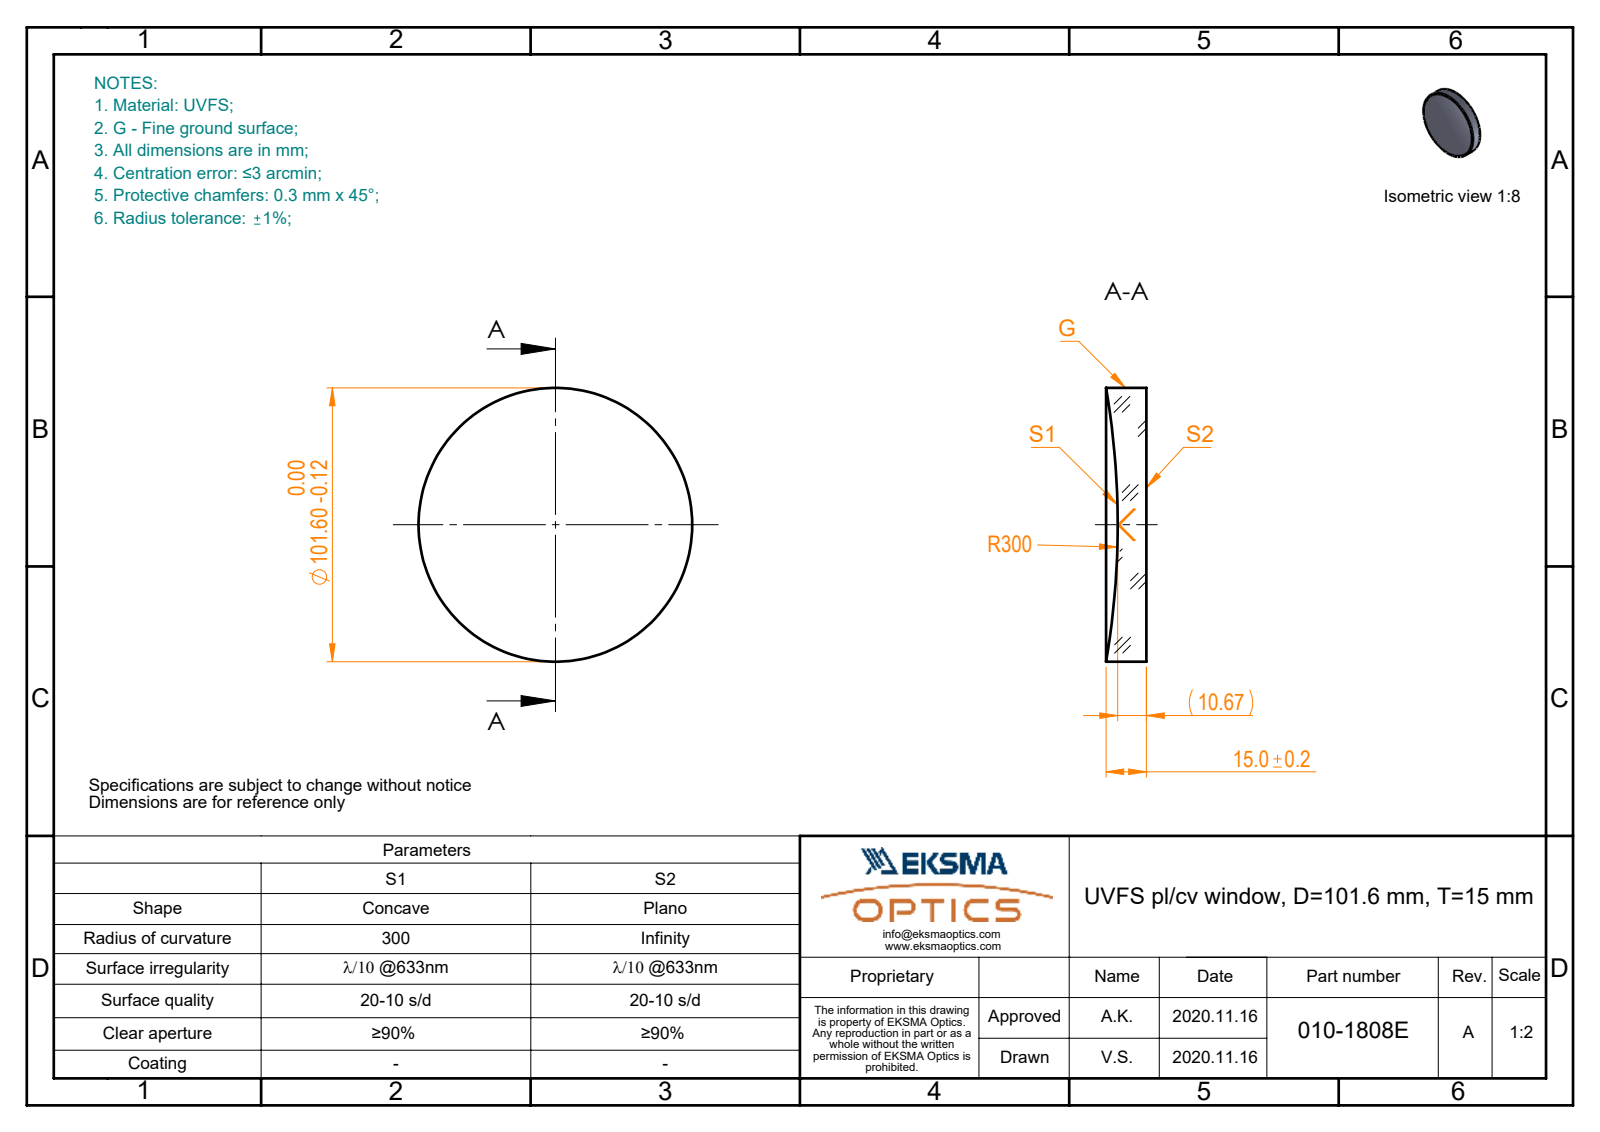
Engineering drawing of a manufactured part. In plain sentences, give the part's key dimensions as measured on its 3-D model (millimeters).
The part is named "010-1808E_UVFS_PCV_window". Its 3-D file was written by "SolidWorks 2019 (CONFIG_CONTROL_DESIGN)". It is 1 solid with 5 faces: 1 planar, 2 cylindrical and 2 other. Overall it measures 101.6 by 101.6 by 15 millimeters. Its volume is 104 005 cubic millimeters and its surface area 21 061 square millimeters. Round bosses or shafts: 1 of diameter 101.6.
